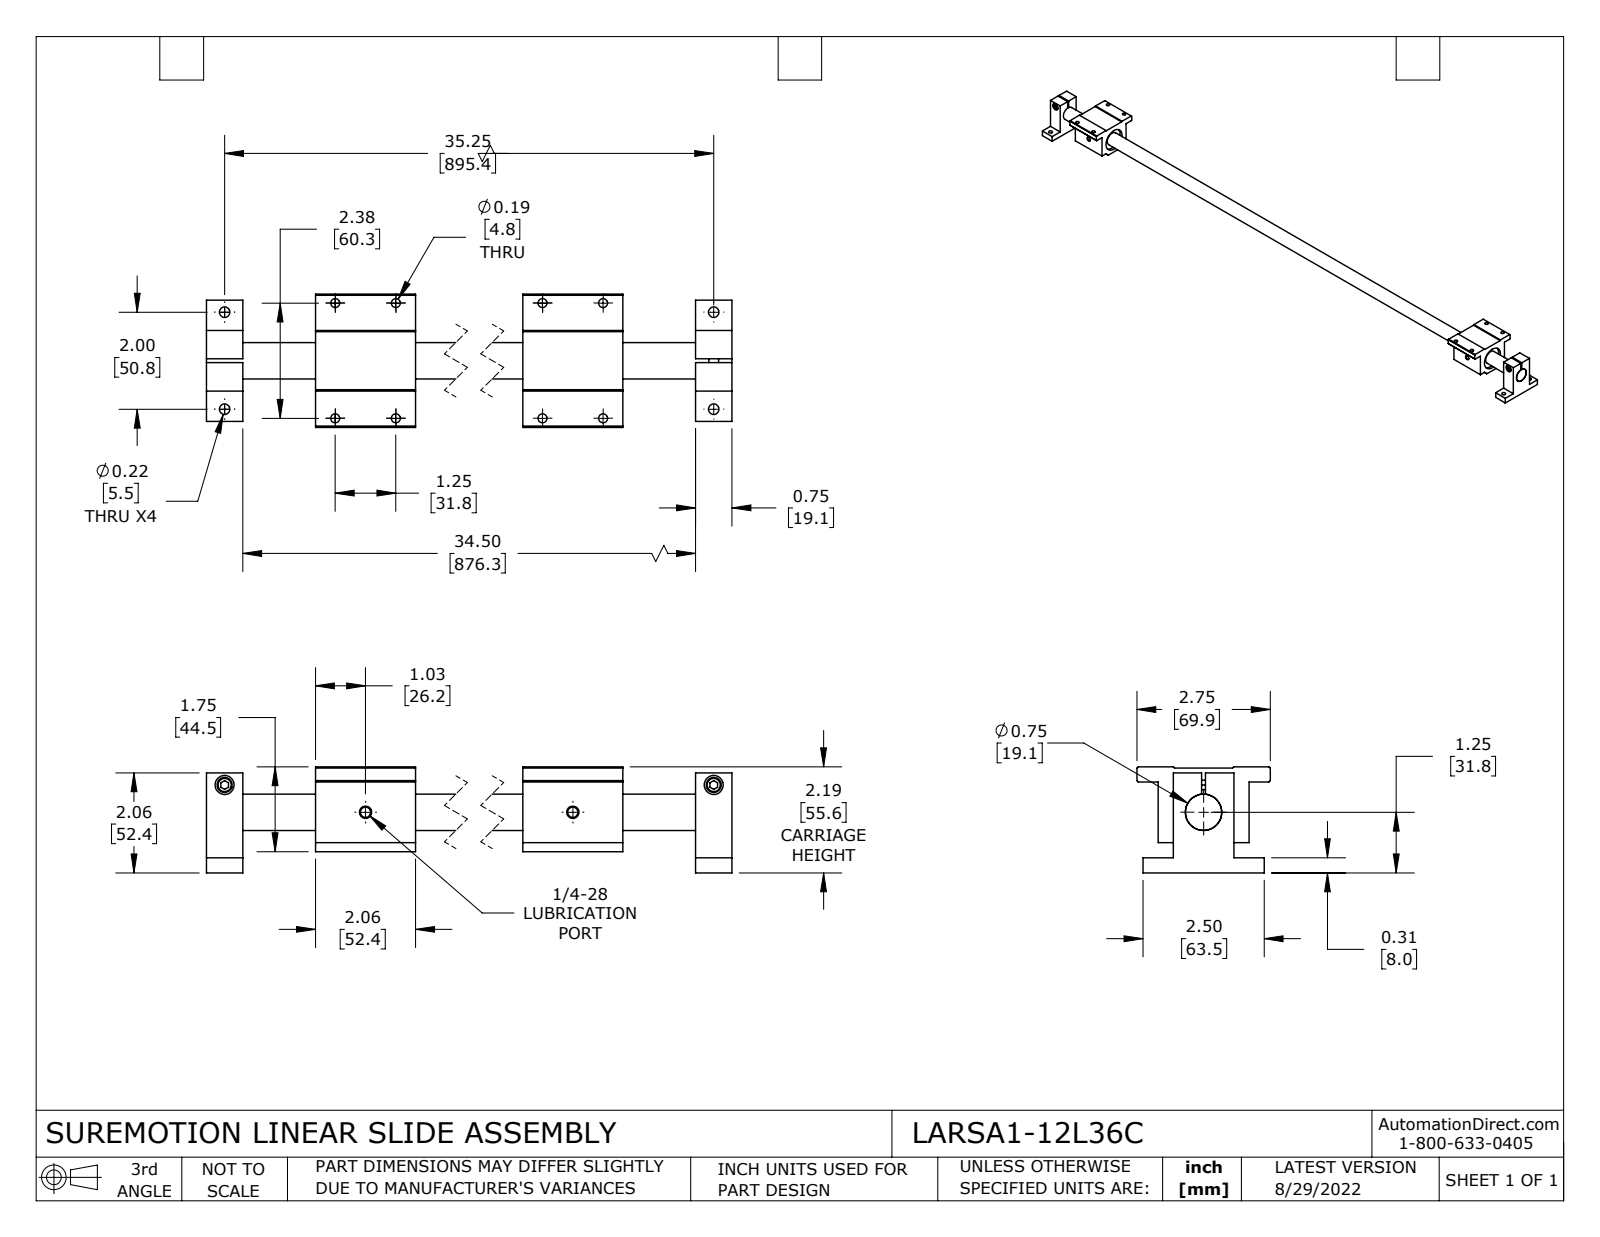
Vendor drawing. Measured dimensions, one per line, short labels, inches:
name: LARSA1-12L36C-RAIL; LARSACC-002; LARSA1-12L36C
written by: SolidWorks 2021 (CONFIG_CONTROL_DESIGN)
unit: in
bodies: 7 solids, 166 faces (98 planar, 58 cylindrical, 10 other)
size: 36 × 2.75 × 2.187
volume: 31.09 in³; area: 175.7 in²
holes: 8× ⌀0.188, 4× ⌀0.218, 2× ⌀0.213, 2× ⌀0.394, 1× ⌀0.75, 1× ⌀1.25
bosses: 2× ⌀0.312
face distances: 1.563, 0.75, 2.063, 29.437, 1.75, 0.313, 1.876, 35.25, 0.028, 0.313
hole spacings: 29.437, 1.25, 2.376, 2.684, 29.533, 35.25, 2, 2.289
